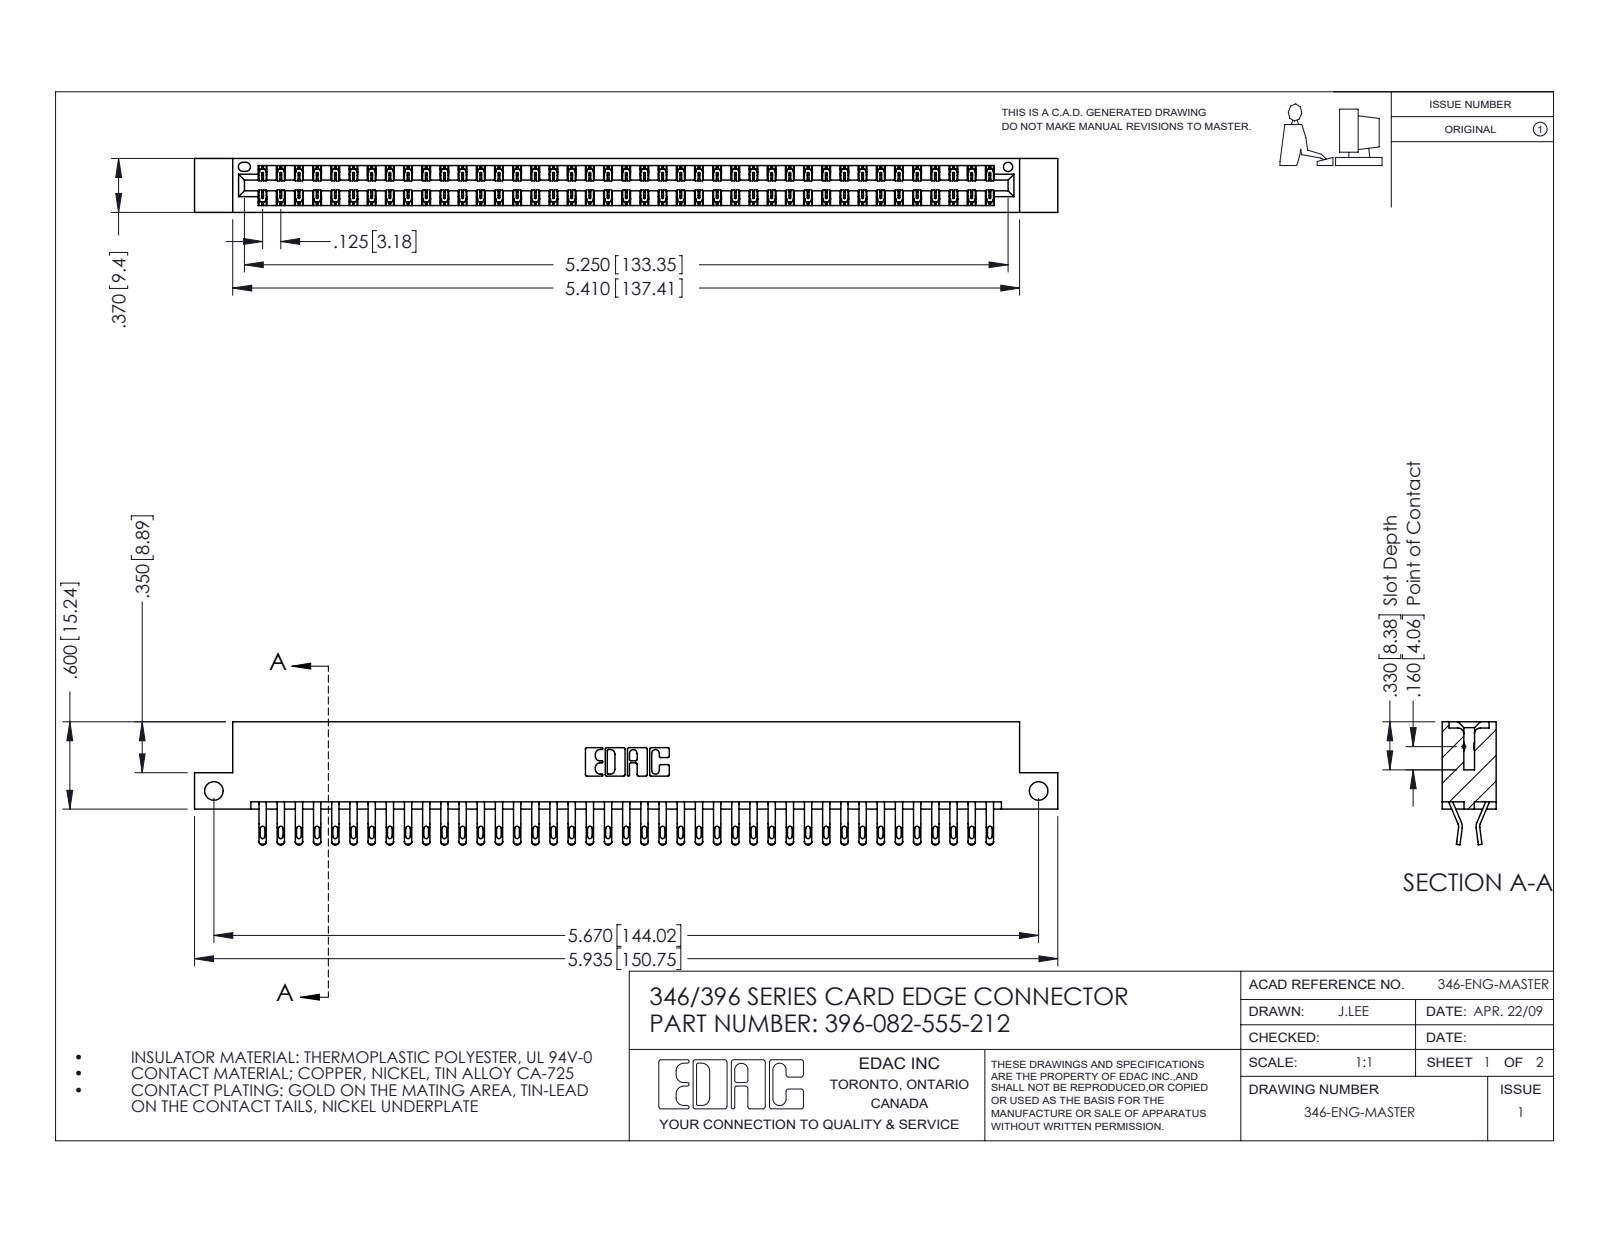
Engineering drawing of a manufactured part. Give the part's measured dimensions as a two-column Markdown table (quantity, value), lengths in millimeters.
| quantity | value |
| --- | --- |
| part name | 396-082-555-212; 346 Part_Flush Mounting Lugs - Side Mount; 345-292-001_555 Tail |
| STEP written by | SolidWorks 2016 (CONFIG_CONTROL_DESIGN) |
| units | millimeters |
| bodies | 83 solids, 4878 faces (2782 planar, 2096 cylindrical, 0 other) |
| overall size | 150.7 × 21.5 × 9.4 |
| volume | 14 800 mm³ |
| surface area | 21 100 mm² |
| round holes (diameter × count) | 3.3 × 2, 1.6 × 1 |
| partial cylindrical surfaces (radius × count) | 0.4 × 164, 0.5 × 164, 0.2 × 123, 0.3 × 22, 0.2 × 6, 0.8 × 6, 0.7 × 3, 0.3 × 2 |
| main face-to-face distances | 1.2, 8.2, 9.4, 6.4, 0.6, 1.8, 7.6, 7, 3.8, 5.6 |
| hole center spacings | 144 |
